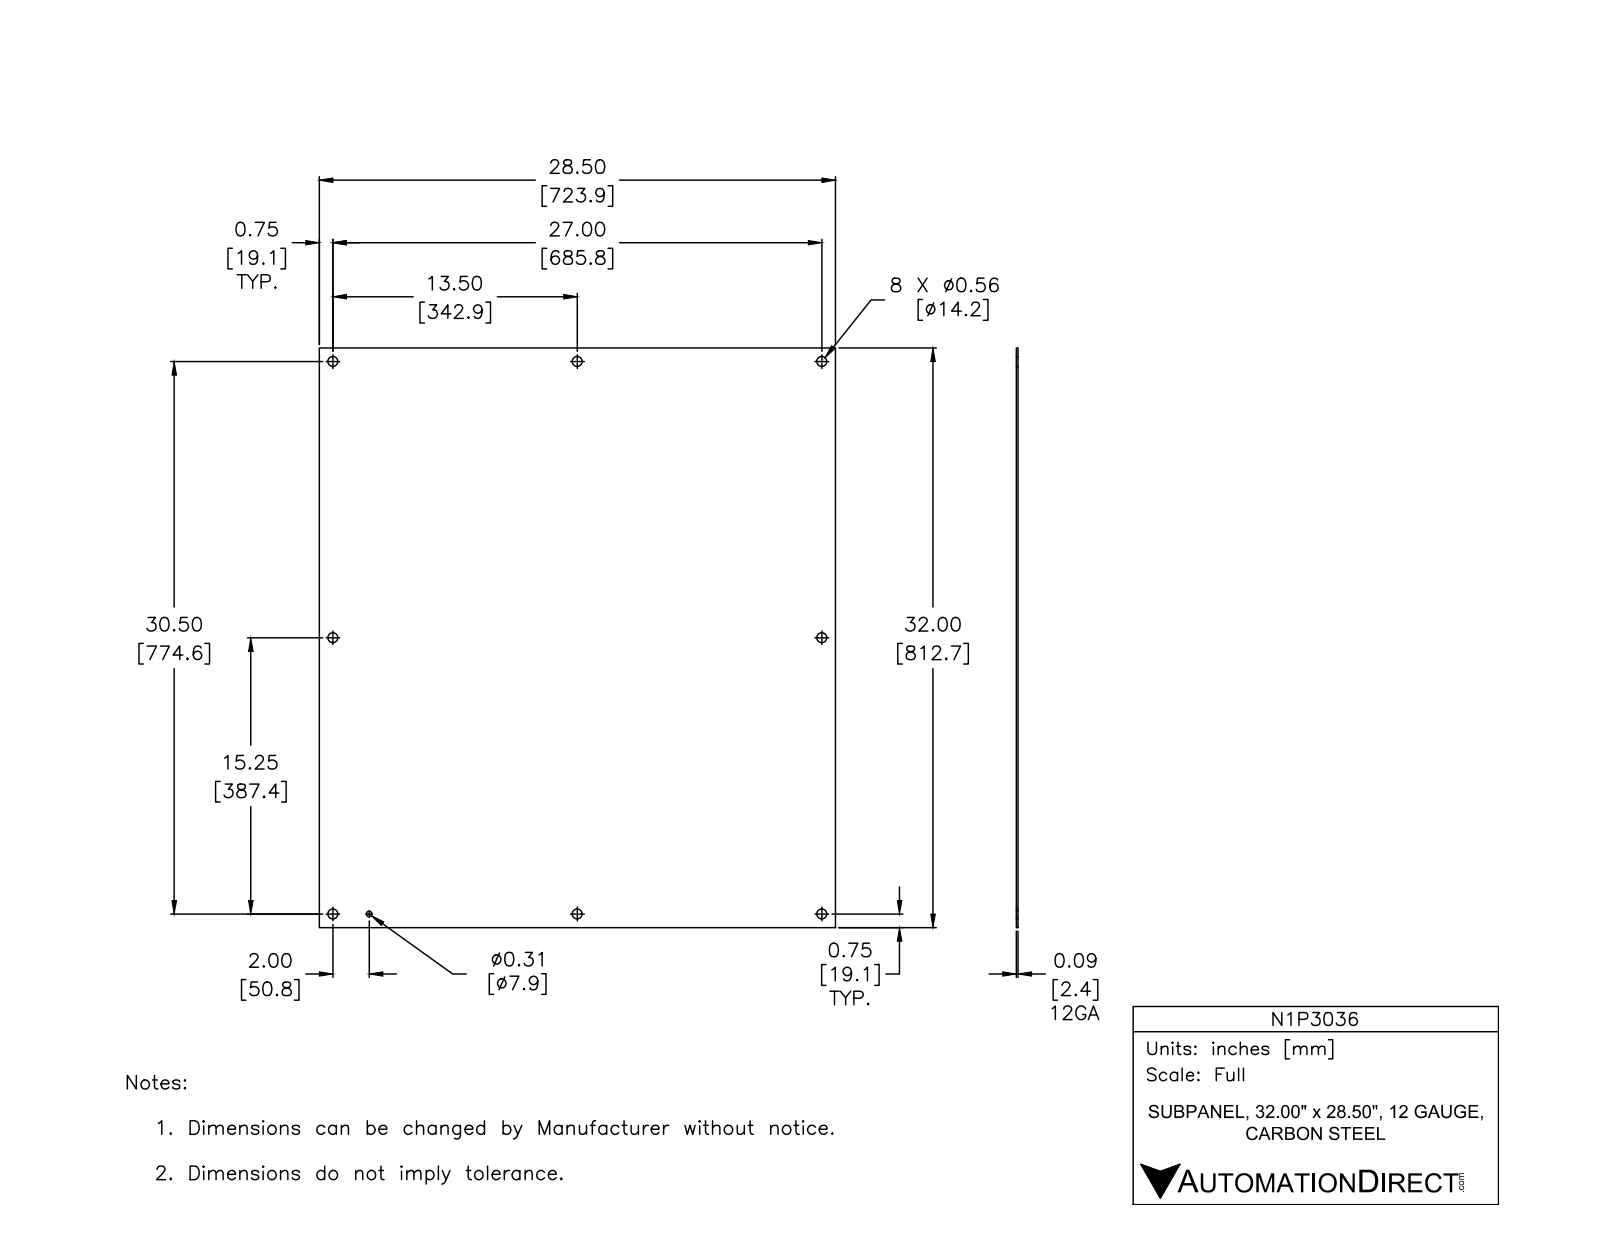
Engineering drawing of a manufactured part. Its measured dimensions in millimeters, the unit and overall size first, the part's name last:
Units: millimetres
Overall size (bounding box): 812.8 × 723.9 × 2.4
Round holes (diameter × count): ⌀14.3 ×8, ⌀7.9 ×1
Main face-to-face distances: 2.4, 723.9, 812.8
Hole centre spacings: 342.9, 387.4, 517.3, 787.6, 847.2, 685.8, 774.7, 1034.6
Volume: 1 398 000 mm³ · Surface area: 1 183 000 mm²
Bodies: 1 solid, 15 faces (6 planar, 9 cylindrical, 0 other)
Part name (STEP PRODUCT): N1P3036-1
STEP written by: Autodesk Inventor 2012 (AUTOMOTIVE_DESIGN)
